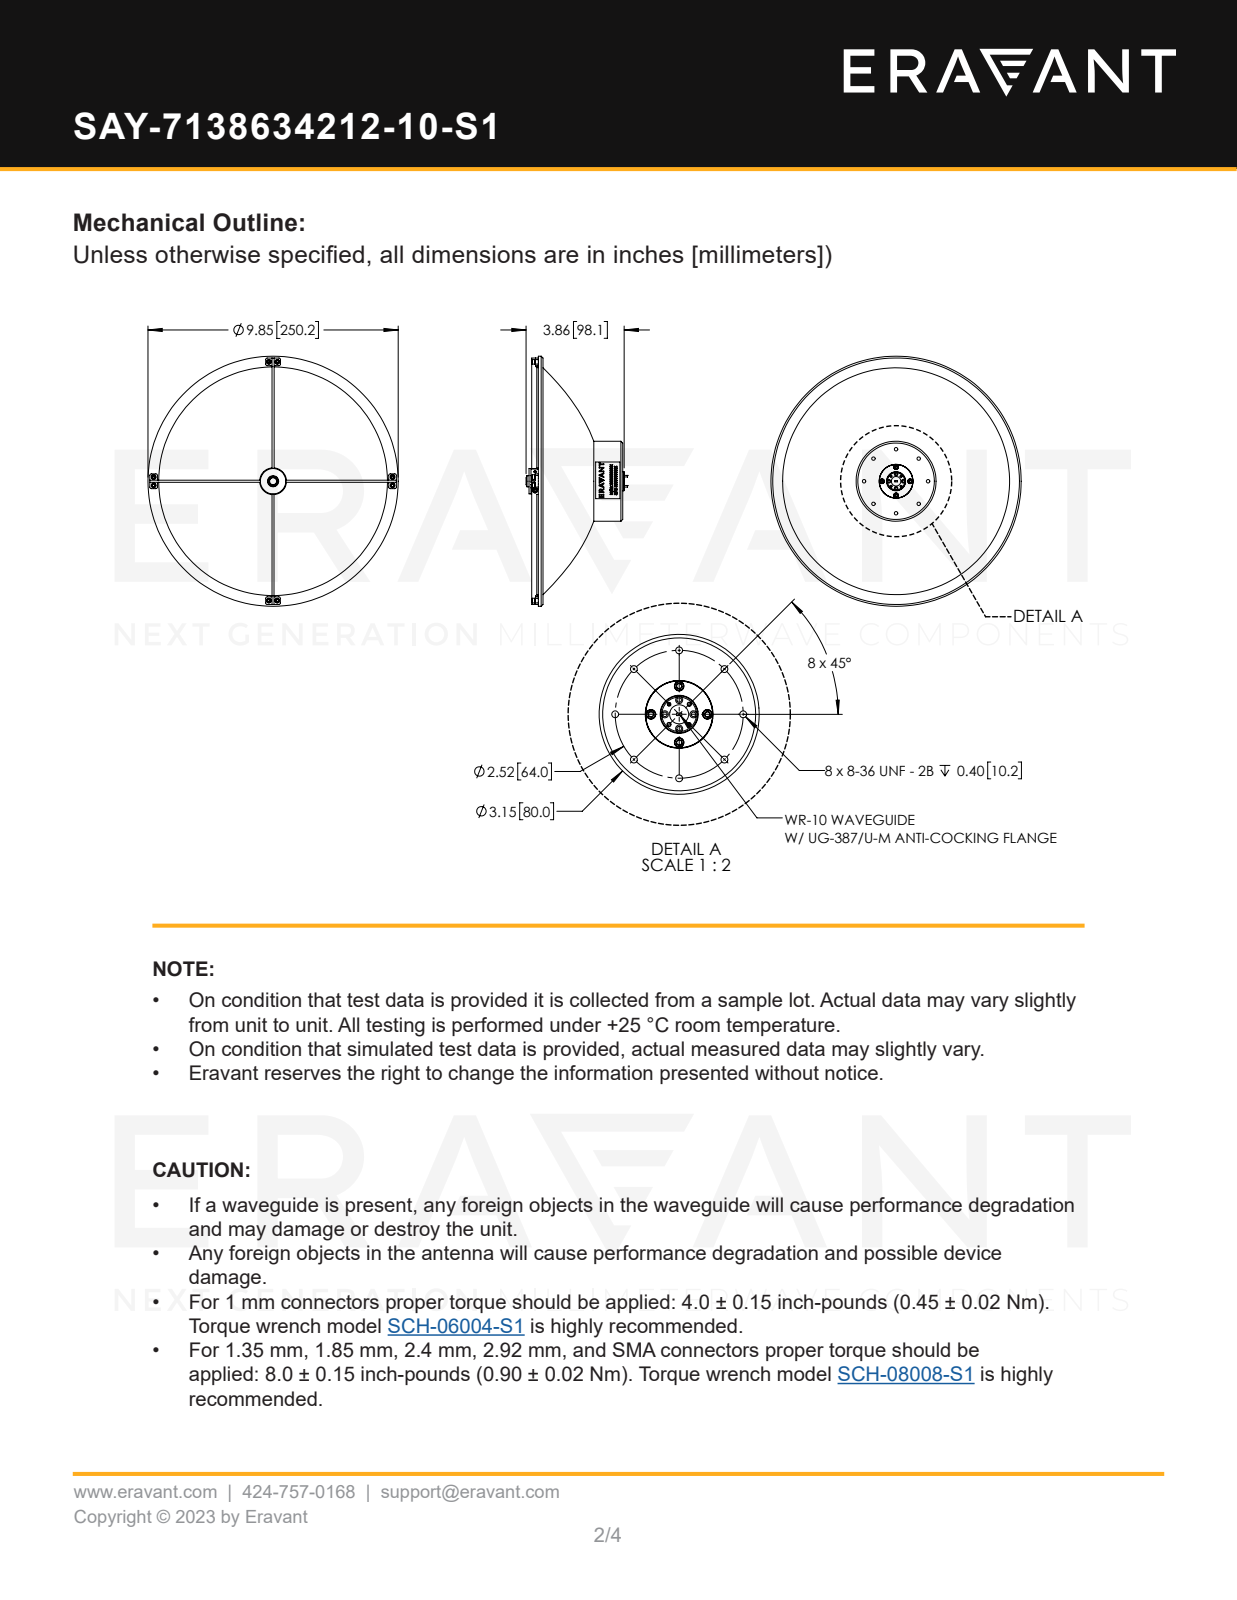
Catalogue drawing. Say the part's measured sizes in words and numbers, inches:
The part is named "SAY-7138634212-10-S1". Its 3-D file was written by "SolidWorks 2021 (CONFIG_CONTROL_DESIGN)". It is 46 solids with 1297 faces: 488 planar, 393 cylindrical and 416 other. Overall it measures 9.85 by 9.85 by 3.995 inches. Its volume is 19.09 cubic inches and its surface area 234.1 square inches. Round holes: 24 of diameter 0.089, 16 of diameter 0.12, 8 of diameter 0.136, 4 of diameter 0.14, 4 of diameter 0.188, 2 of diameter 0.061, 2 of diameter 0.067, 1 of diameter 0.063, 1 of diameter 0.317, 1 of diameter 0.68, 1 of diameter 0.755, 1 of diameter 1.335. Round bosses or shafts: 20 of diameter 0.112, 16 of diameter 0.183, 16 of diameter 0.18, 4 of diameter 0.07, 4 of diameter 0.063, 1 of diameter 9.85, 1 of diameter 3.15, 1 of diameter 1.325. Partial cylindrical surfaces (rounded edges, fillets, slot ends): 24 of radius 0.005, 24 of radius 0.06, 8 of radius 0.02, 8 of radius 0.04, 1 of radius 0.25. The main face-to-face distances are 0.184, 3.137, 3.321, 0.079, 0.225, 2.912, 3.096, 3.581, 3.356, 0.444. The hole center spacings are 1.08, 1.291, 1.472, 0.215, 0.281, 0.398, 0.408, 0.519.
